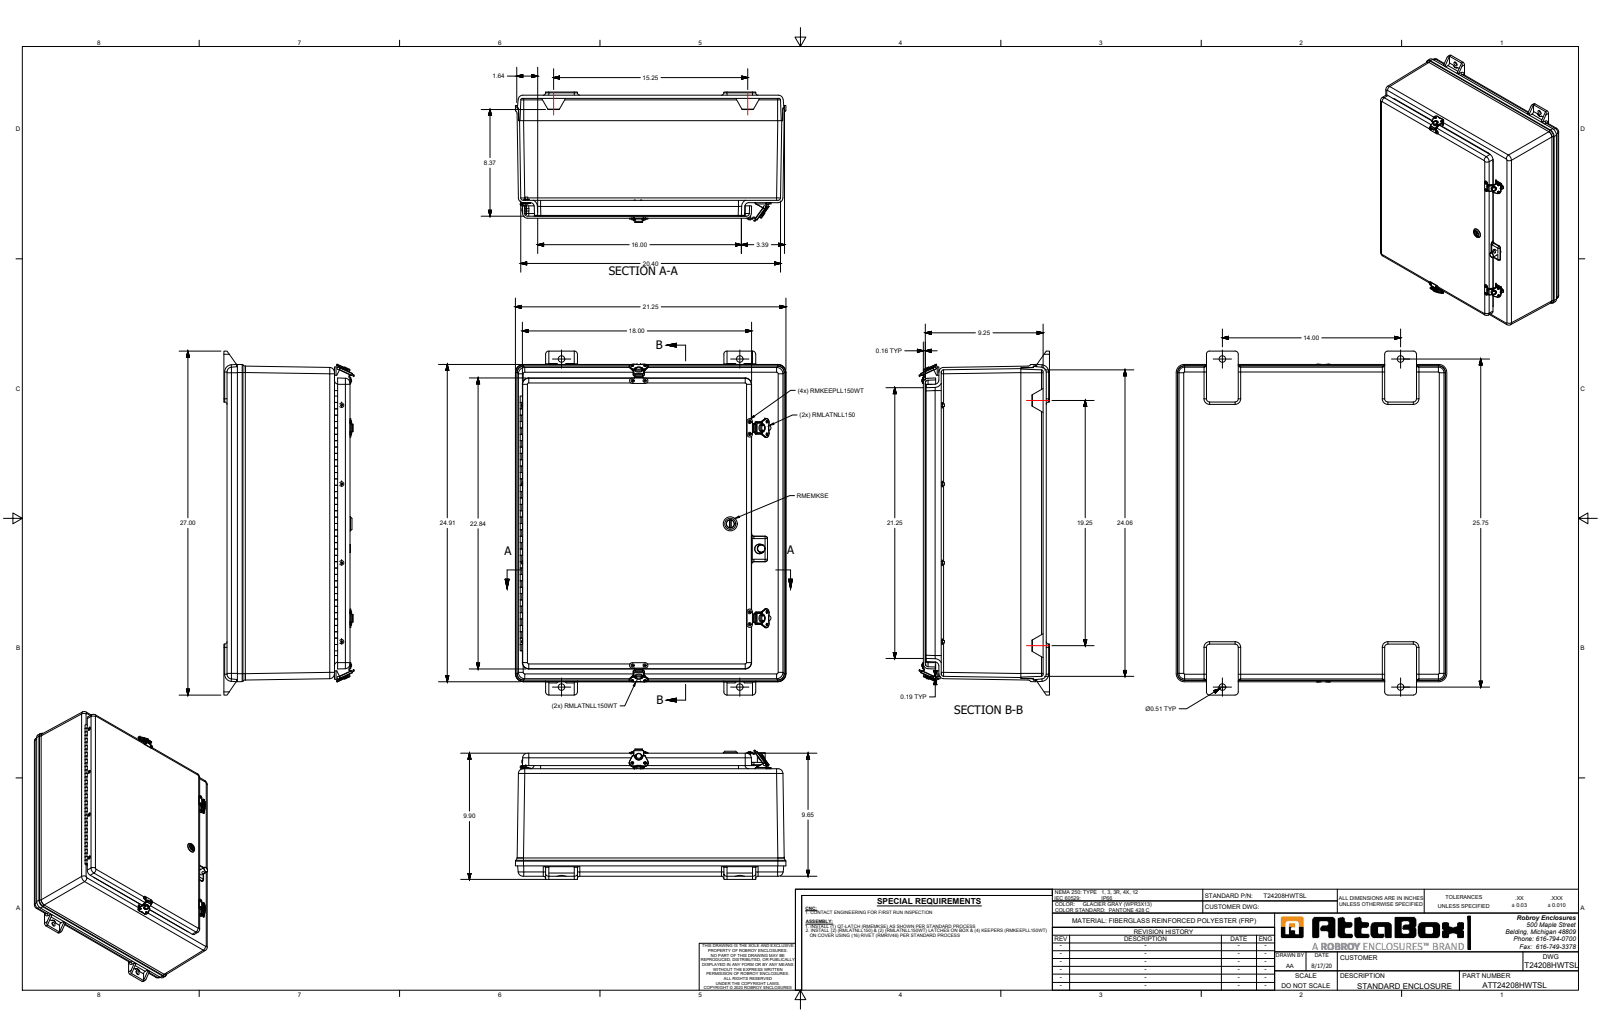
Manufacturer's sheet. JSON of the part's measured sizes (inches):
{"part_name": "T24208HWTSL", "step_written_by": "SolidWorks 2019 (AUTOMOTIVE_DESIGN)", "units": "inches", "bodies": {"solids": 66, "faces": 1848, "planar": 746, "cylindrical": 729, "other": 373}, "overall_size": [27, 21.25, 10.239], "volume_in3": 411.1, "surface_area_in2": 4378, "round_holes": [[0.13, 28], [0.063, 16], [0.1, 8], [0.138, 8], [0.187, 8], [0.201, 8], [0.208, 4], [0.563, 4], [0.135, 3], [0.156, 3], [0.145, 2], [0.51, 2]], "round_bosses_or_shafts": [[0.14, 16], [0.357, 8], [0.187, 8], [0.5, 4], [0.438, 4], [0.2, 3], [0.135, 3], [0.281, 2]], "partial_cylinders_radius": [[0.01, 101], [0.012, 30], [0.25, 24], [0.03, 16], [0.375, 16], [0.187, 13], [0.02, 12], [0.5, 12]], "face_to_face_distances": [0.25, 0.186, 9.498, 9.248, 0.156, 9.655, 9.405, 8.436, 1.405, 8.25], "hole_center_spacings": [0.937, 1, 1.453, 3.309, 14.938, 14.981, 22.508, 26.835]}
